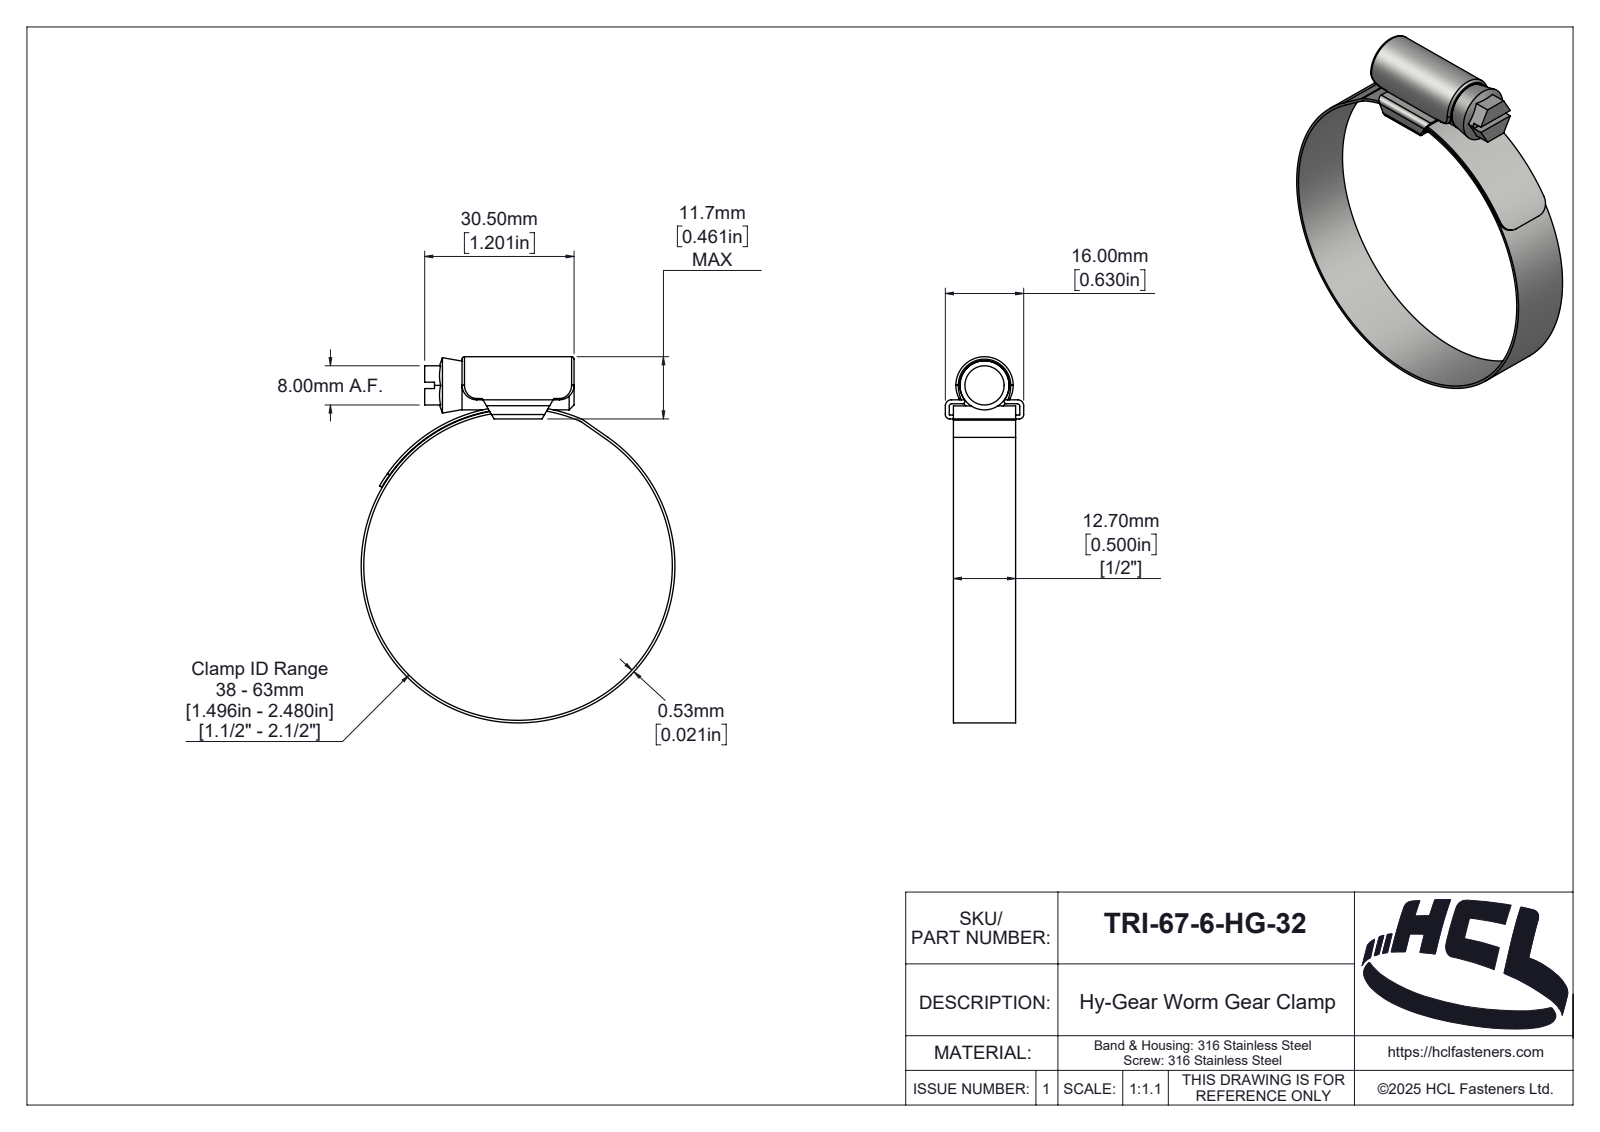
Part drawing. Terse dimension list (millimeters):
name: TRI-57-0-HG-32
written by: SolidWorks 2025 (AUTOMOTIVE_DESIGN)
unit: mm
bodies: 3 solids, 189 faces (39 planar, 89 cylindrical, 61 other)
size: 74.73 × 64.06 × 16
volume: 4 565 mm³; area: 9 091 mm²
holes: 1× ⌀63
bosses: 1× ⌀64.06, 1× ⌀10
rounds: 6× R0.5, 4× R3, 2× R0.1, 2× R0.9, 2× R1.2, 1× R0.46, 1× R1.89, 1× R2
face distances: 0.8, 3.1, 12.7, 0.53, 2.3, 3.9, 30.5, 1.65, 14.35, 15.2
